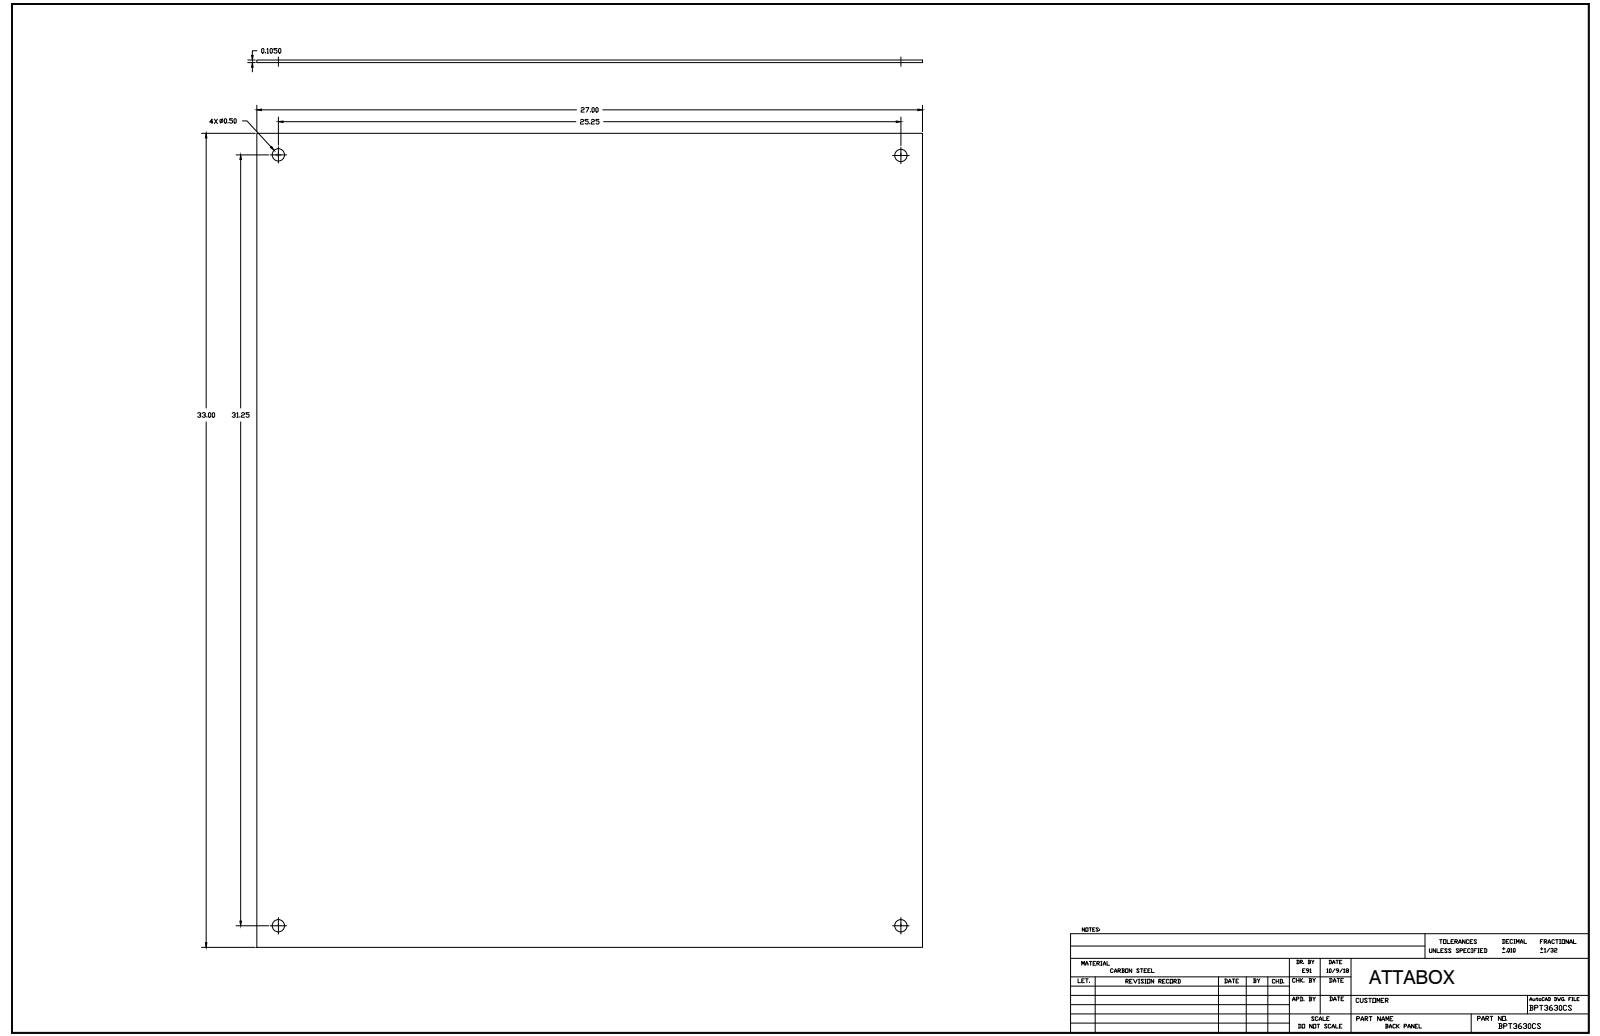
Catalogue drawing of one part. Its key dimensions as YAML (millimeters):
part_name: "BP3630CS_STP"
step_written_by: "Autodesk Inventor 2014 (AUTOMOTIVE_DESIGN)"
units: millimeters
bodies: {solids: 1, faces: 12, planar: 6, cylindrical: 6, other: 0}
overall_size: [838.2, 685.8, 2.67]
volume: 1531000
surface_area: 1157000
round_holes:
  - {diameter: 12.7, count: 6}
face_to_face_distances: [2.66, 685.8, 838.2]
hole_center_spacings: [396.88, 754.21, 641.34, 793.76, 1020.48]
